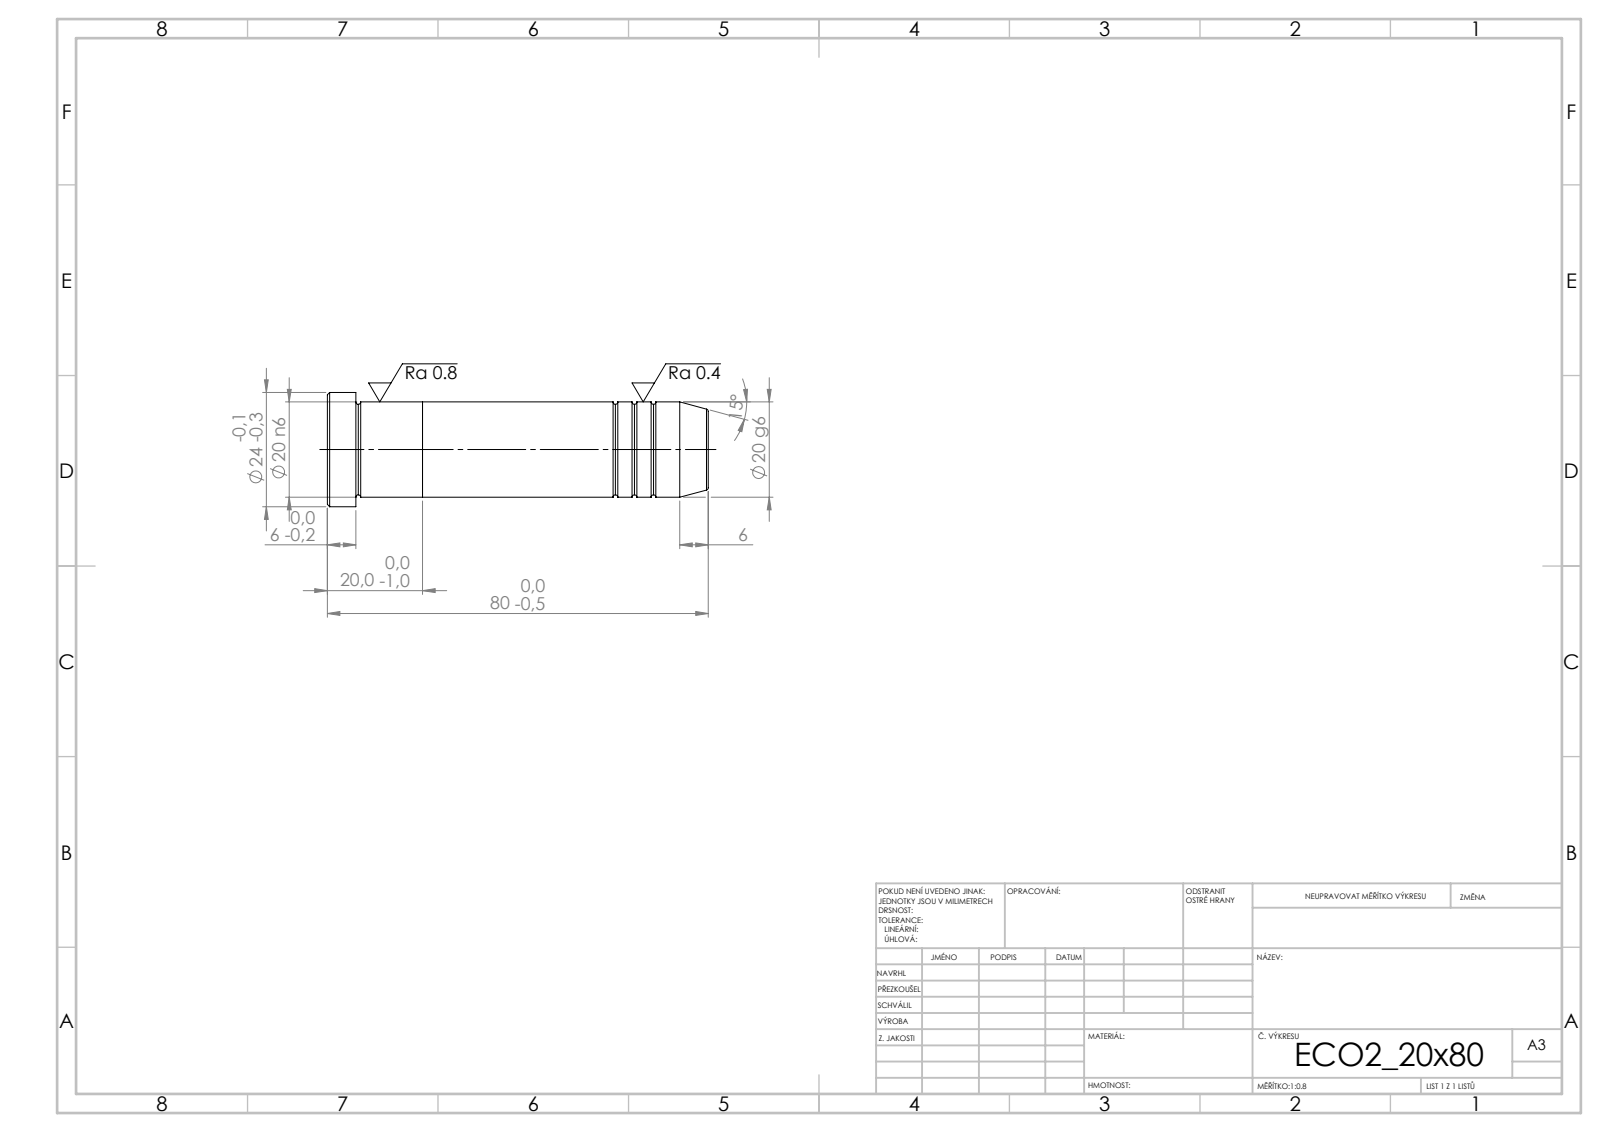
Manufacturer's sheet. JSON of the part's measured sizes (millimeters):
{"step_written_by": "SolidWorks 2019 (CONFIG_CONTROL_DESIGN)", "units": "millimeters", "bodies": {"solids": 2, "faces": 39, "planar": 5, "cylindrical": 12, "other": 22}, "overall_size": [80, 24, 24], "volume_mm3": 25568, "surface_area_mm2": 6627, "round_bosses_or_shafts": [[24, 1], [20, 1]], "face_to_face_distances": [20, 60, 80, 74, 14, 6]}
